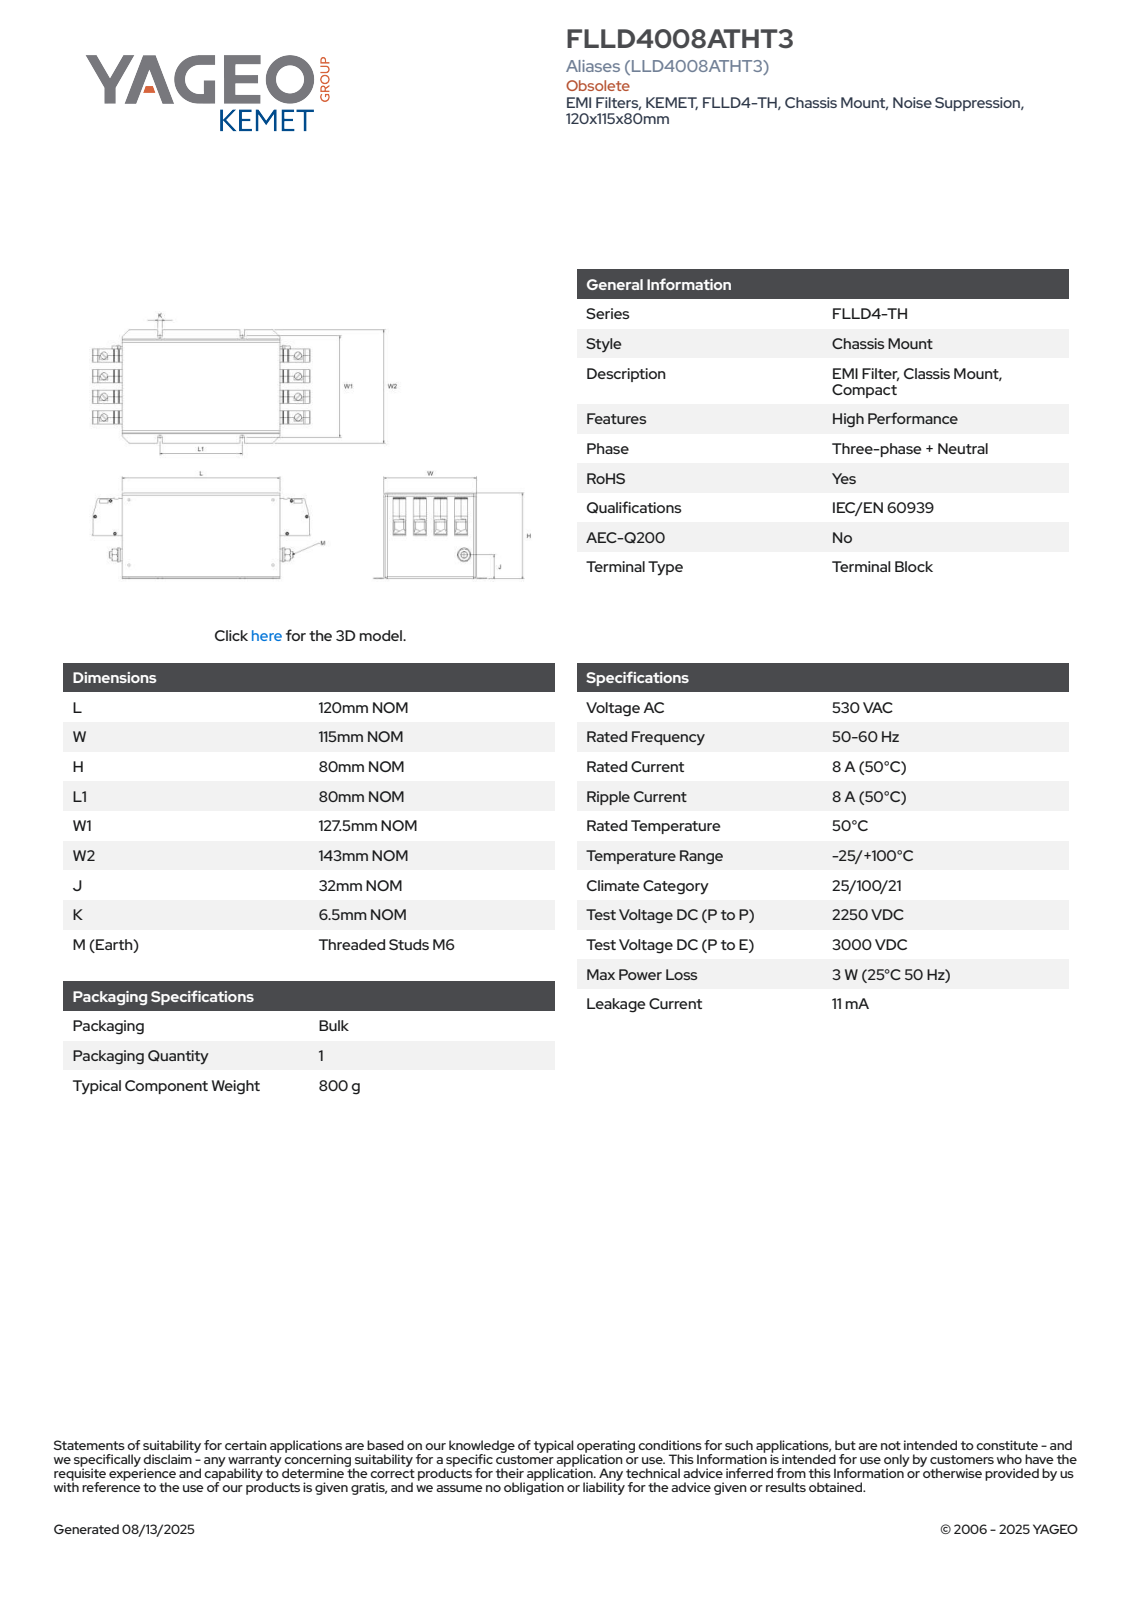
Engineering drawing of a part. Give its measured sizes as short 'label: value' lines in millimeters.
name: hex nut style 1 gradeab_din_Hexagon Nut ISO 4032 - M6 - D - N; KLE0130_MPT1010; plain washer grade a_din_Washer DIN 125 - A 6.4; GEH0664 (+6 more)
written by: SolidWorks 2014 (AUTOMOTIVE_DESIGN)
unit: mm
bodies: 30 solids, 3710 faces (2286 planar, 1200 cylindrical, 224 other)
size: 154.8 × 143 × 80.18
volume: 75 456 mm³; area: 179 942 mm²
holes: 8× ⌀3.3, 8× ⌀3.85, 8× ⌀7.5, 4× ⌀2, 4× ⌀3.4, 4× ⌀7.2, 4× ⌀7.4, 4× ⌀8, 1× ⌀4.13, 1× ⌀5, 1× ⌀6, 1× ⌀6.4
bosses: 8× ⌀3.5, 4× ⌀9, 4× ⌀7, 4× ⌀3.2, 4× ⌀1.8, 1× ⌀12, 1× ⌀11, 1× ⌀10
rounds: 130× R0.1, 41× R0.2, 16× R0.49, 16× R1.3, 12× R1, 12× R2, 8× R2.5, 4× R3.25
face distances: 1, 79.18, 114, 119, 80.18, 78.18, 113, 120, 115, 118
hole spacings: 15, 30, 17.76, 136.33, 2.13, 9.5, 31.47, 45
